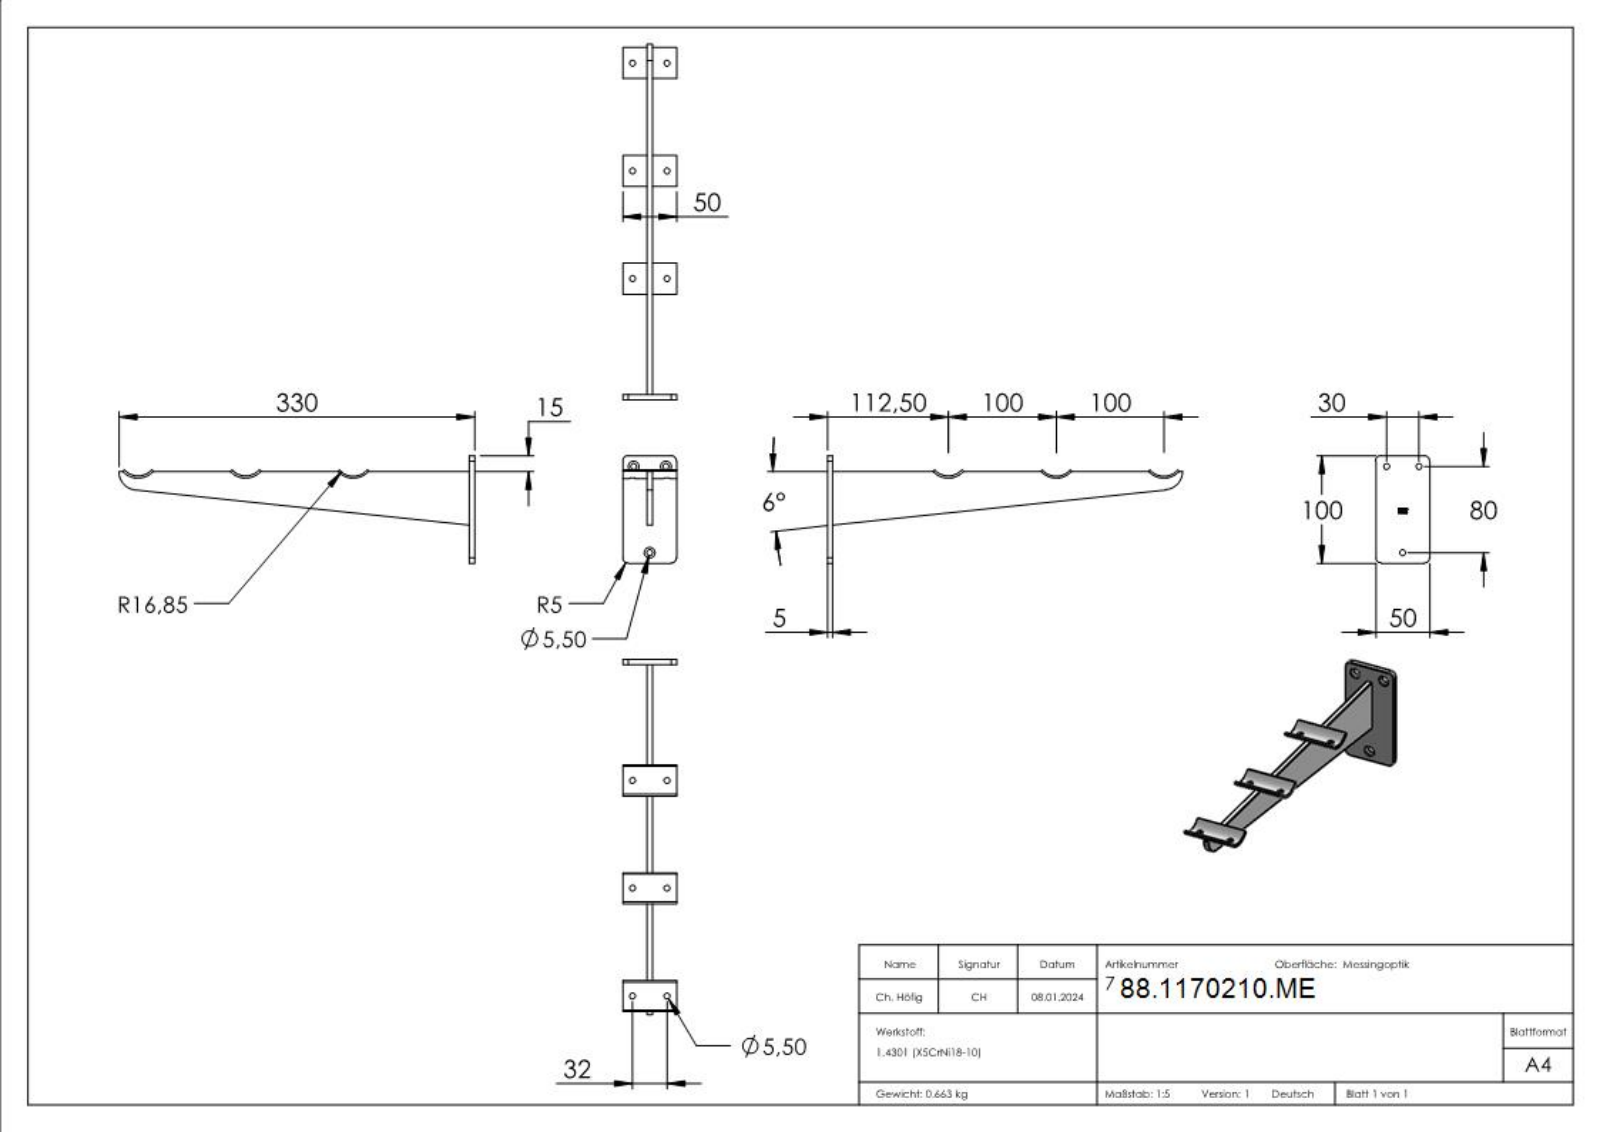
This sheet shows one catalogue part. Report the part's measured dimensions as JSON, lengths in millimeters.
{"part_name": "70210-ME", "step_written_by": "SolidWorks 2018 (CONFIG_CONTROL_DESIGN)", "units": "millimeters", "bodies": {"solids": 1, "faces": 245, "planar": 147, "cylindrical": 23, "other": 75}, "overall_size": [330, 100, 50], "volume_mm3": 83934, "surface_area_mm2": 44215, "round_holes": [[5.5, 9], [10, 3]], "partial_cylinders_radius": [[5, 4], [16.85, 3], [18.85, 3], [17.01, 1]], "face_to_face_distances": [5, 22.5, 27.5, 50, 64.4, 85, 100, 15, 128.8, 4.9], "hole_center_spacings": [100, 105, 32, 81.39, 200, 202.54, 30]}
